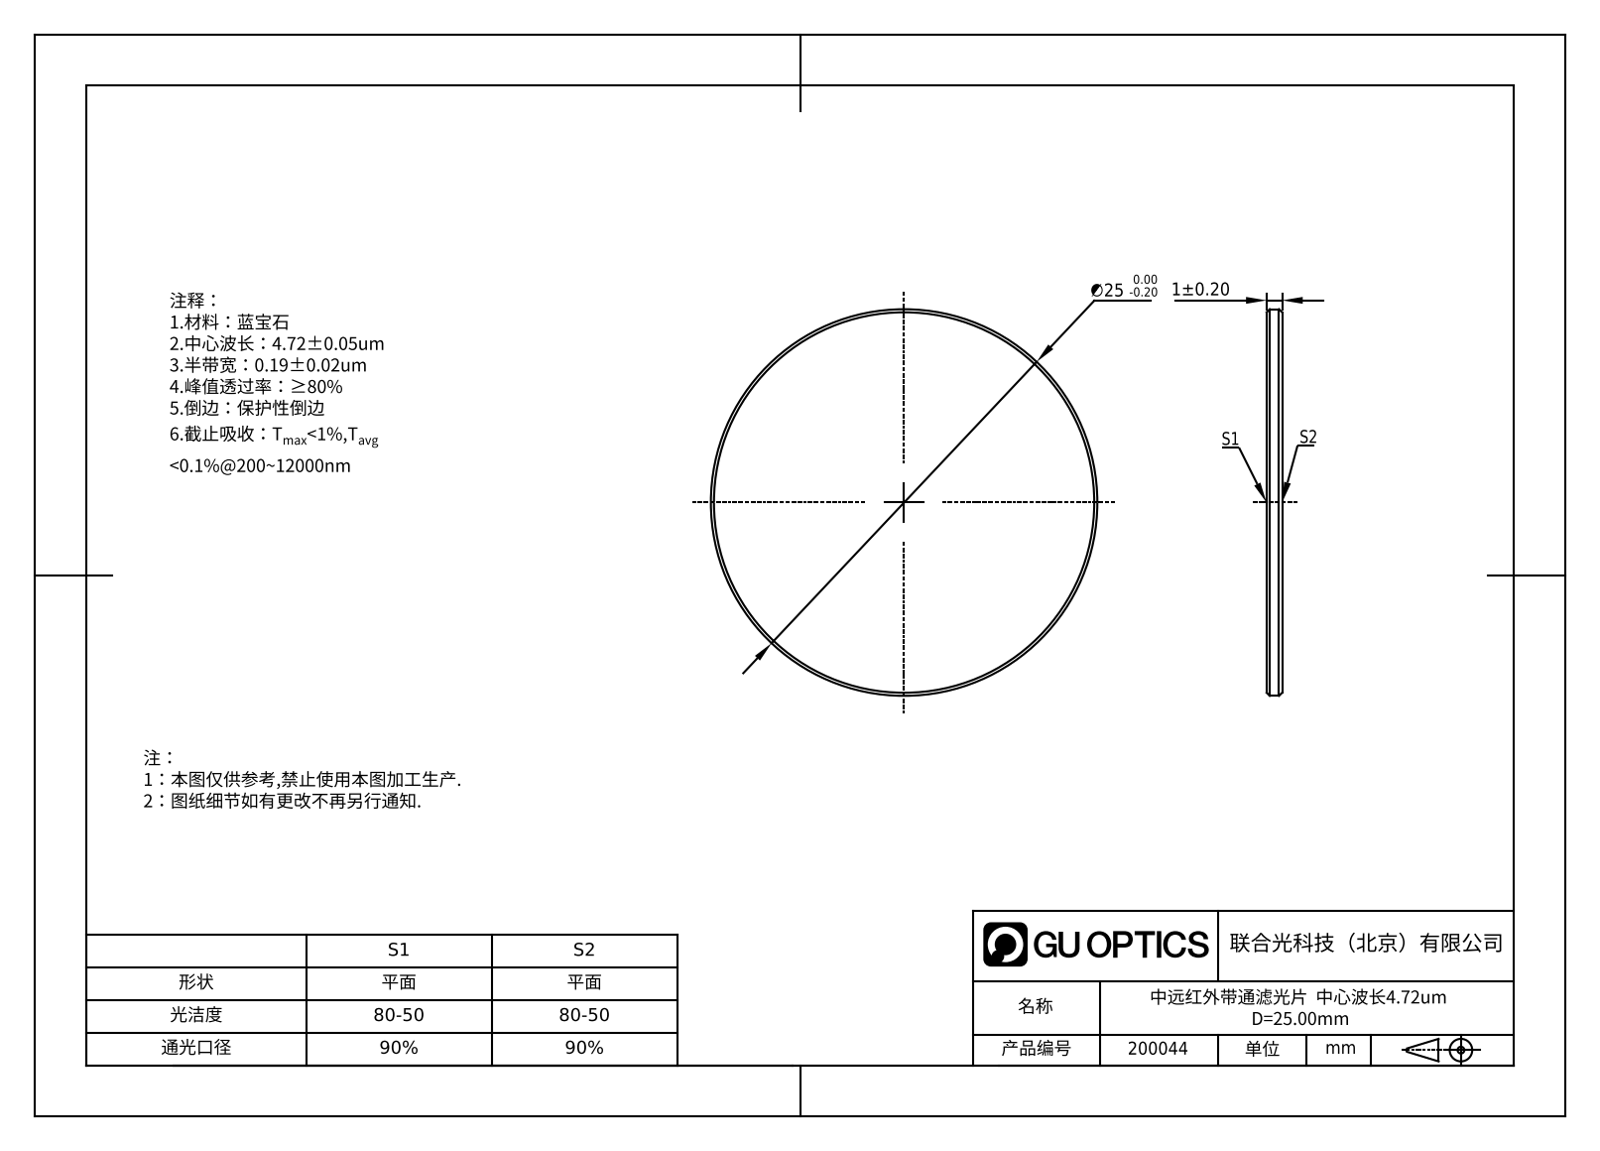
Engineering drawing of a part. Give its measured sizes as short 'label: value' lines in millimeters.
name: GNIF-190-4720-D25
written by: SolidWorks 2022 (AUTOMOTIVE_DESIGN)
unit: mm
bodies: 1 solid, 8 faces (2 planar, 2 cylindrical, 4 other)
size: 25 × 25 × 1
volume: 488 mm³; area: 1 042 mm²
bosses: 1× ⌀25
face distances: 1
